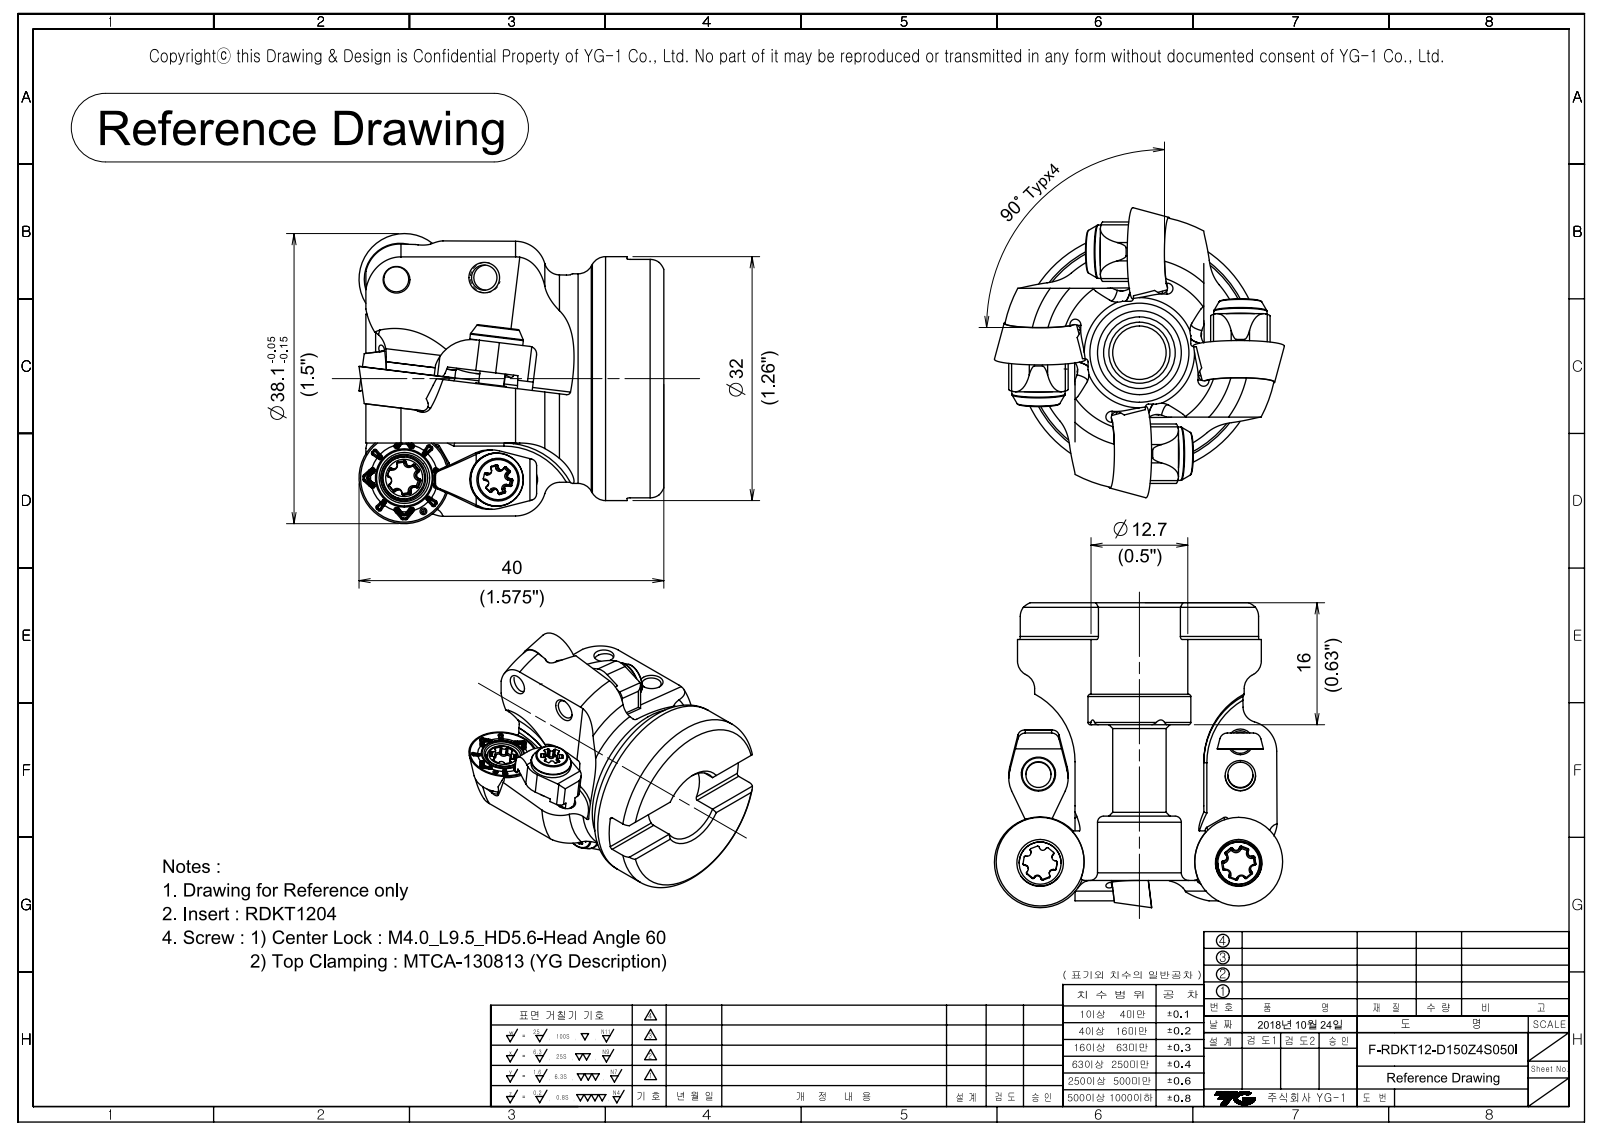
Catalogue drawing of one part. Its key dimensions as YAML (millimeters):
part_name: "CUTTER_F-RDKT12-D150Z4S050I"
step_written_by: "SIEMENS PLM Software NX 10.0 (CONFIG_CONTROL_DESIGN)"
units: millimeters
bodies: {solids: 17, faces: 2581, planar: 308, cylindrical: 306, other: 1967}
overall_size: [40.01, 38.06, 38.06]
volume: 20495
surface_area: 12459
round_holes:
  - {diameter: 2.5, count: 4}
  - {diameter: 3, count: 4}
  - {diameter: 3.3, count: 4}
  - {diameter: 3.5, count: 4}
  - {diameter: 4.4, count: 4}
  - {diameter: 4.5, count: 4}
  - {diameter: 7.01, count: 1}
  - {diameter: 11, count: 1}
  - {diameter: 12.7, count: 1}
  - {diameter: 13.5, count: 1}
round_bosses_or_shafts:
  - {diameter: 4, count: 8}
  - {diameter: 7, count: 4}
  - {diameter: 5.5, count: 4}
  - {diameter: 4.3, count: 4}
  - {diameter: 32, count: 1}
  - {diameter: 27.5, count: 1}
partial_cylinders:
  - {radius: 0.15, count: 96}
  - {radius: 0.3, count: 24}
  - {radius: 0.45, count: 24}
  - {radius: 0.4, count: 22}
  - {radius: 1.5, count: 20}
  - {radius: 1, count: 12}
  - {radius: 0.5, count: 8}
  - {radius: 0.75, count: 8}
face_to_face_distances: [4.4, 16.9, 10.1, 4, 5.7, 6.1, 1.7, 5.07, 11.83, 3.97]
hole_center_spacings: [4.47, 11.39, 11.5, 15.86, 15.97]
